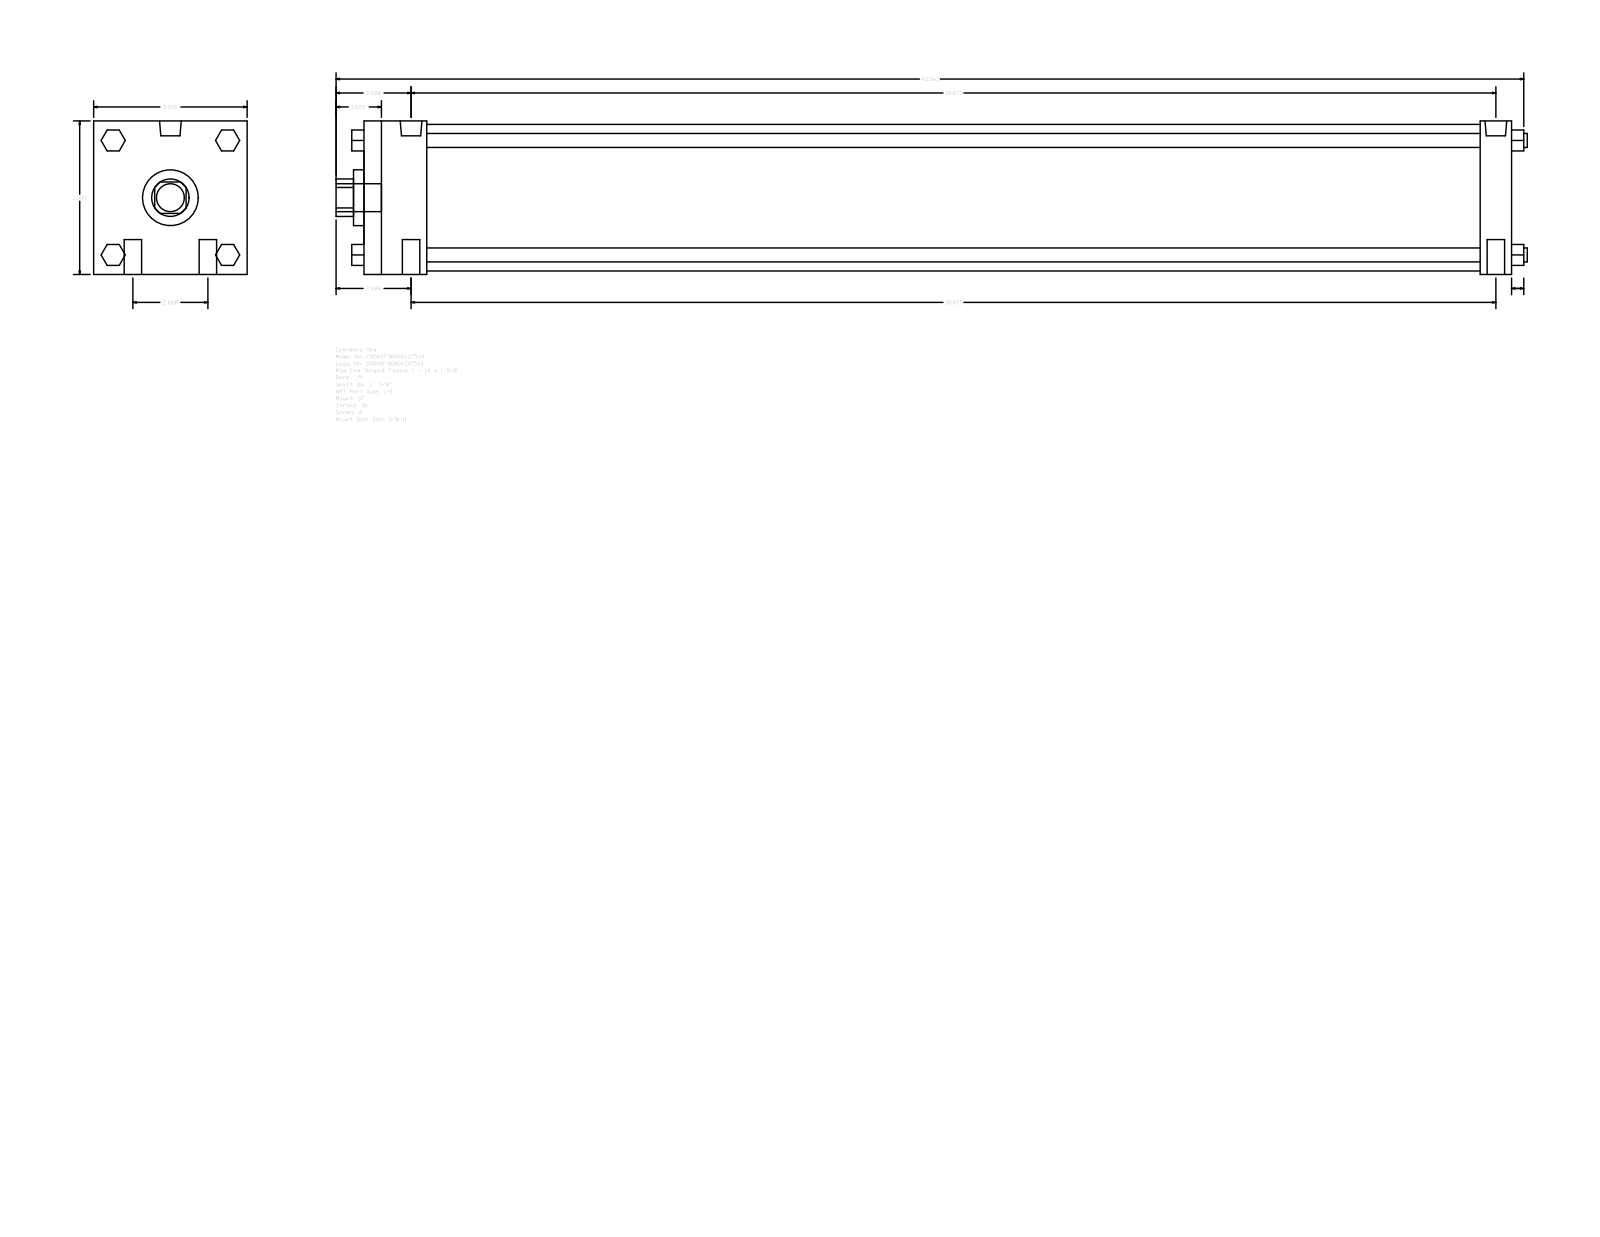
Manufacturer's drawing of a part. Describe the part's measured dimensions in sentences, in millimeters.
The part is named "A_SF__0500_1.375". Its 3-D file was written by "GSSL Pune (CONFIG_CONTROL_DESIGN)". It is 0 solids with 124 faces: 94 planar, 30 cylindrical and 0 other. Overall it measures 1084.26 by 139.7 by 139.7 millimeters. Round holes: 1 of diameter 34.92, 1 of diameter 50.8, 1 of diameter 133.35. Round bosses or shafts: 4 of diameter 15.88, 4 of diameter 12.7, 2 of diameter 19.77, 2 of diameter 8.73, 1 of diameter 25.4. Partial cylindrical surfaces (rounded edges, fillets, slot ends): 1 of radius 17.06. The main face-to-face distances are 139.7, 1044.57, 28.57, 57.15, 1016, 958.85, 987.42, 19.05, 52.07, 90.18.
